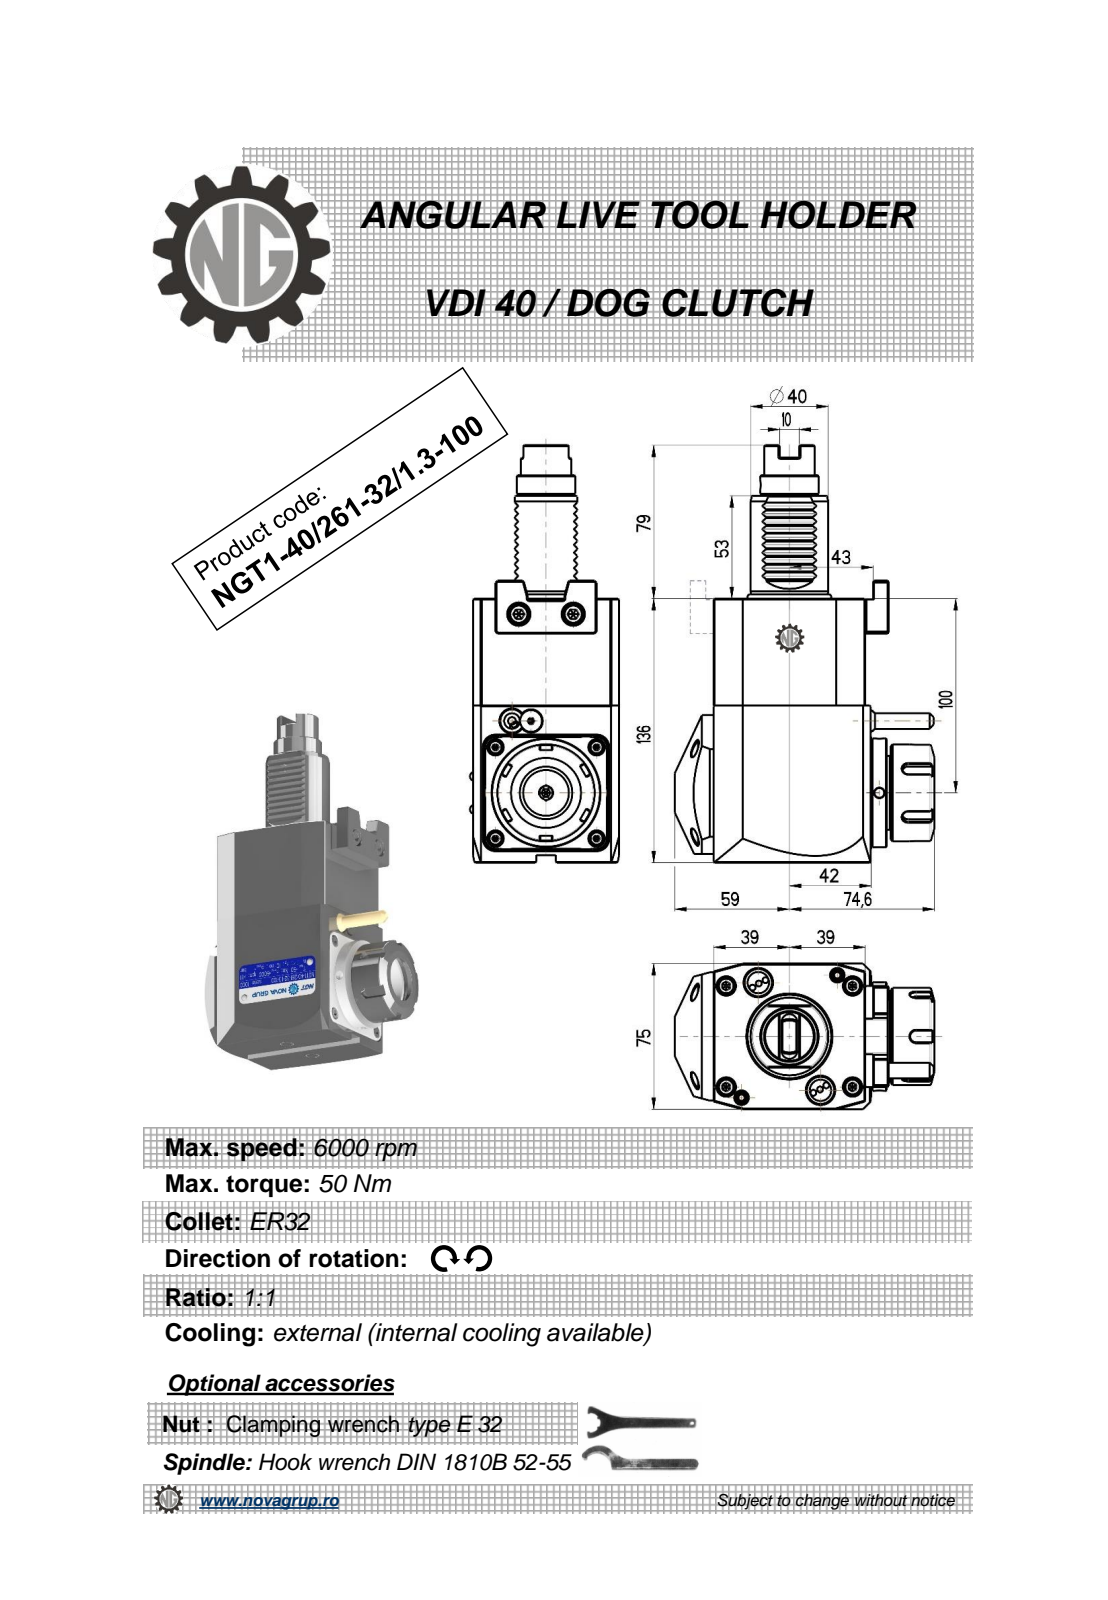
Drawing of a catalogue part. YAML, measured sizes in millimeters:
part_name: "NGT1_40_261_32_1_3_100"
step_written_by: "PRO/ENGINEER BY PARAMETRIC TECHNOLOGY CORPORATION, 2010280 (CONFIG_CONTROL_DESIGN)"
units: millimeters
bodies: {solids: 1, faces: 440, planar: 234, cylindrical: 83, other: 123}
overall_size: [215, 133.6, 76.6]
volume: 999409
surface_area: 77506
round_holes:
  - {diameter: 5, count: 3}
  - {diameter: 3, count: 1}
  - {diameter: 4.2, count: 1}
  - {diameter: 27, count: 1}
round_bosses_or_shafts:
  - {diameter: 56, count: 1}
  - {diameter: 50, count: 1}
  - {diameter: 43, count: 1}
  - {diameter: 40, count: 1}
  - {diameter: 30, count: 1}
  - {diameter: 26, count: 1}
  - {diameter: 11.2, count: 1}
  - {diameter: 8, count: 1}
partial_cylinders:
  - {radius: 0.3, count: 20}
  - {radius: 0.22, count: 6}
  - {radius: 0.26, count: 6}
  - {radius: 3, count: 5}
  - {radius: 0.5, count: 2}
  - {radius: 1, count: 2}
  - {radius: 12.5, count: 1}
  - {radius: 40, count: 1}
face_to_face_distances: [75, 136, 78, 81, 3, 0.5, 84.88, 1, 80.8, 2.8]
hole_center_spacings: [40.93, 122.75, 158.5]
